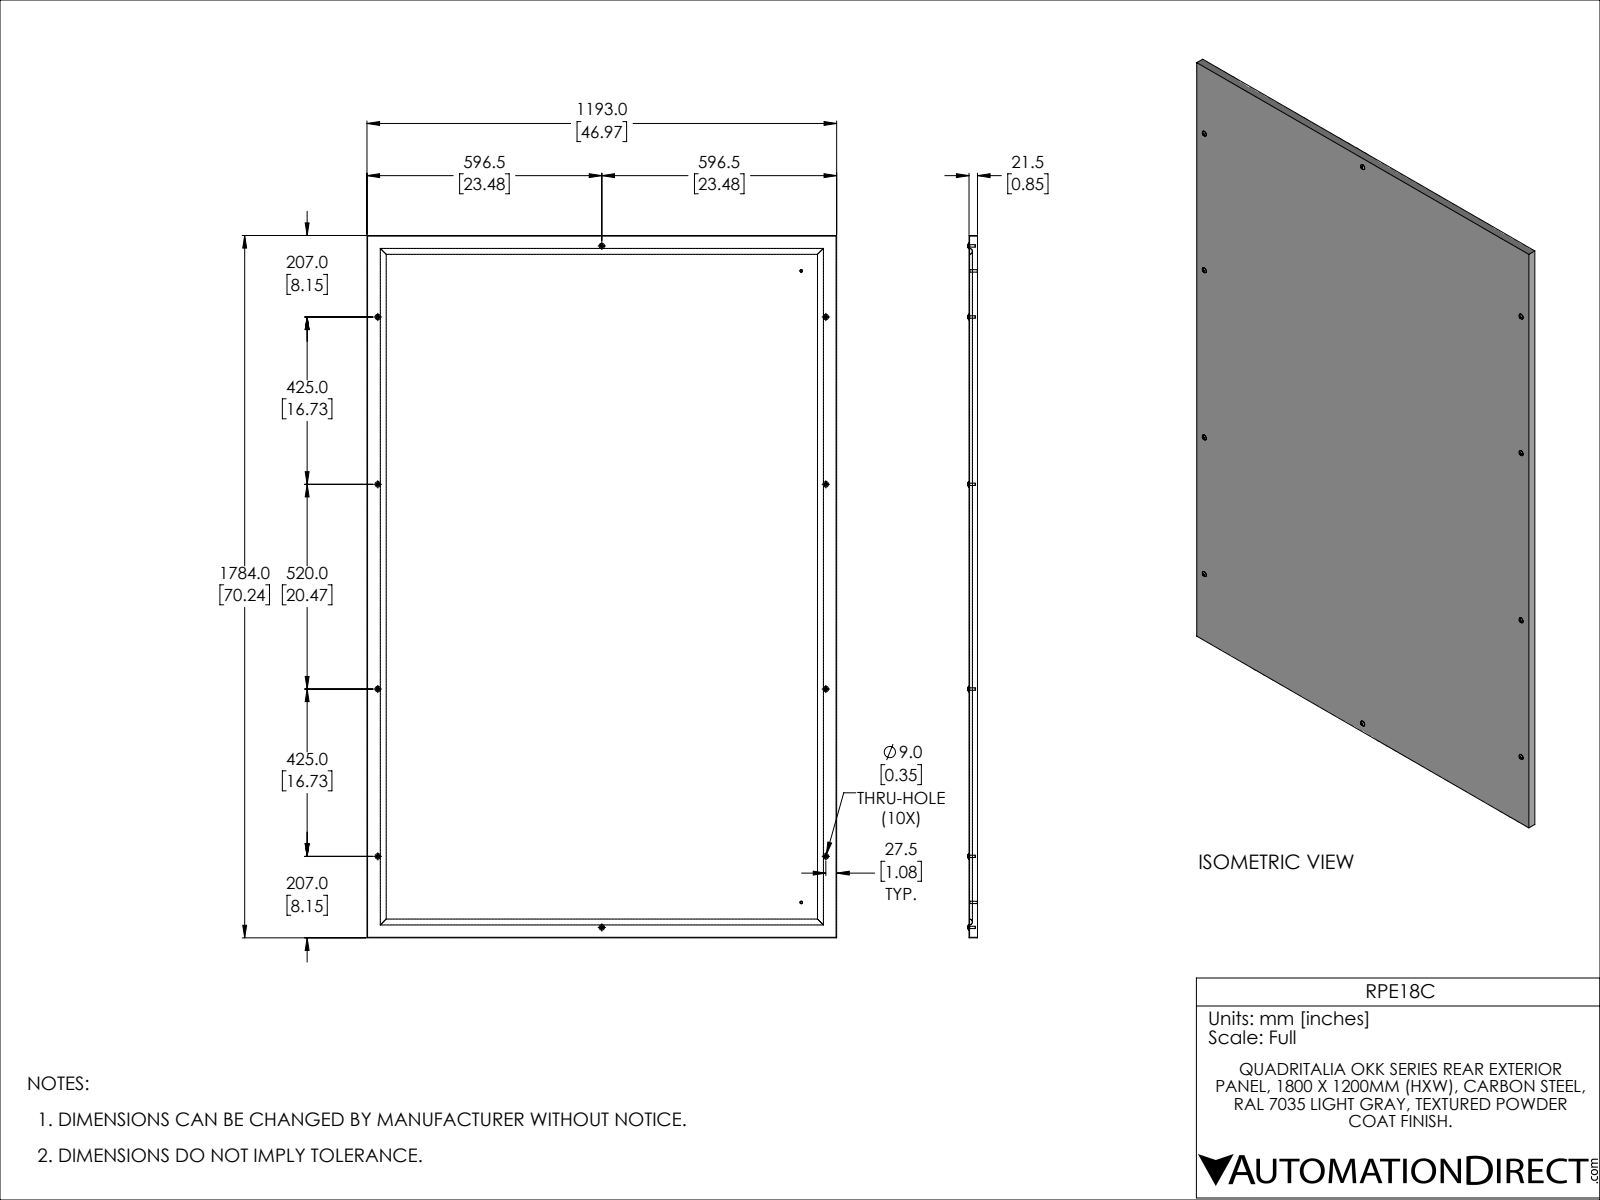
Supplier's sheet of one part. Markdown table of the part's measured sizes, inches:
| quantity | value |
| --- | --- |
| part name | RPE18C |
| STEP written by | SolidWorks 2021 (CONFIG_CONTROL_DESIGN) |
| units | inches |
| bodies | 17 solids, 379 faces (189 planar, 158 cylindrical, 32 other) |
| overall size | 70.236 × 46.969 × 0.992 |
| volume | 234 in³ |
| surface area | 7 321 in² |
| round holes (diameter × count) | 0.354 × 10 |
| round bosses / shafts (diameter × count) | 0.236 × 12, 0.551 × 10, 0.276 × 2 |
| partial cylindrical surfaces (radius × count) | 0.02 × 120, 0.296 × 4 |
| main face-to-face distances | 0.059, 46.909, 70.177, 46.969, 46.85, 70.236, 70.118, 0.846, 0.787, 16.506 |
| hole center spacings | 16.732, 23.502, 32.713, 37.205, 44.803, 47.826, 49.652, 58.237 |
